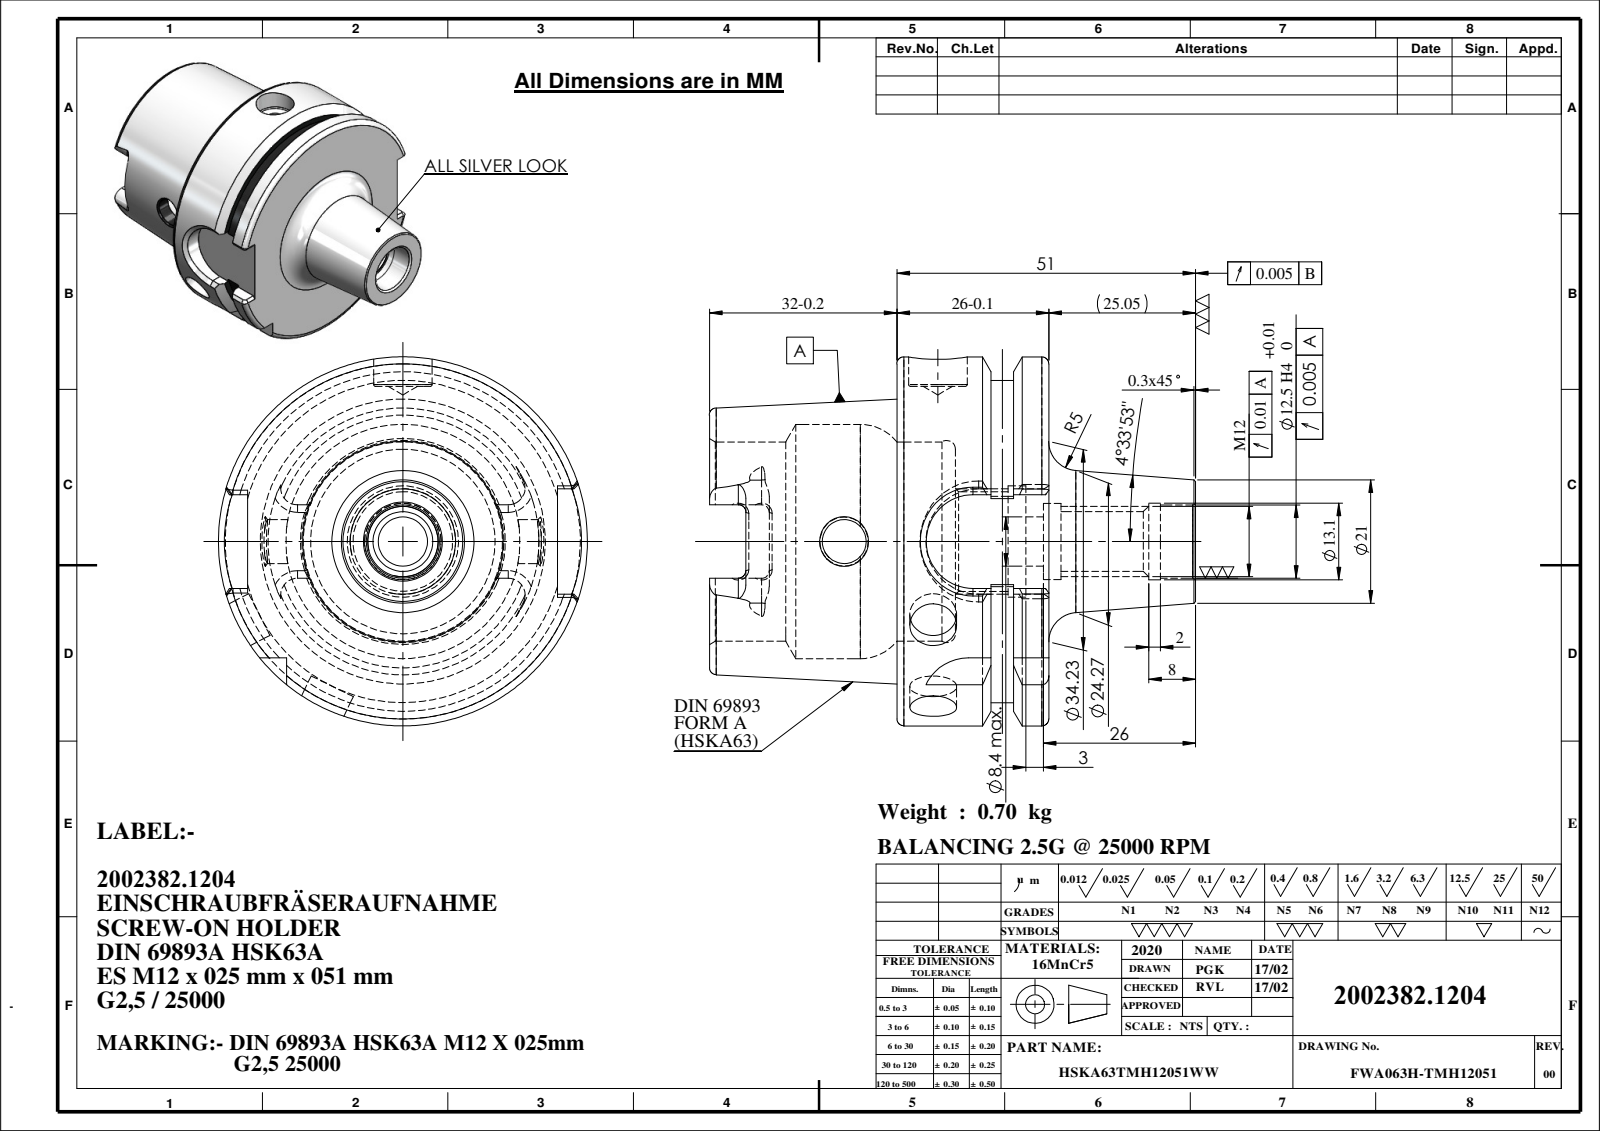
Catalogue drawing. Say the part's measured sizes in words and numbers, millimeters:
The part is named "9163A-ES8M12025". Its 3-D file was written by "SolidWorks 2018 (CONFIG_CONTROL_DESIGN)". It is 1 solid with 172 faces: 53 planar, 53 cylindrical and 66 other. Overall it measures 83 by 63 by 63 millimeters. Its volume is 89 023 cubic millimeters and its surface area 24 867 square millimeters. Round holes: 2 of diameter 8, 1 of diameter 7.5, 1 of diameter 8.4, 1 of diameter 10, 1 of diameter 10.2, 1 of diameter 12.5, 1 of diameter 13, 1 of diameter 13.1, 1 of diameter 17, 1 of diameter 19, 1 of diameter 34, 1 of diameter 40. Round bosses or shafts: 1 of diameter 63, 1 of diameter 55. Partial cylindrical surfaces (rounded edges, fillets, slot ends): 6 of radius 1.3, 4 of radius 2.88, 2 of radius 8, 1 of radius 9. The main face-to-face distances are 25.95, 10, 15.95, 32, 42, 57.95, 52.9, 51, 54, 22.
